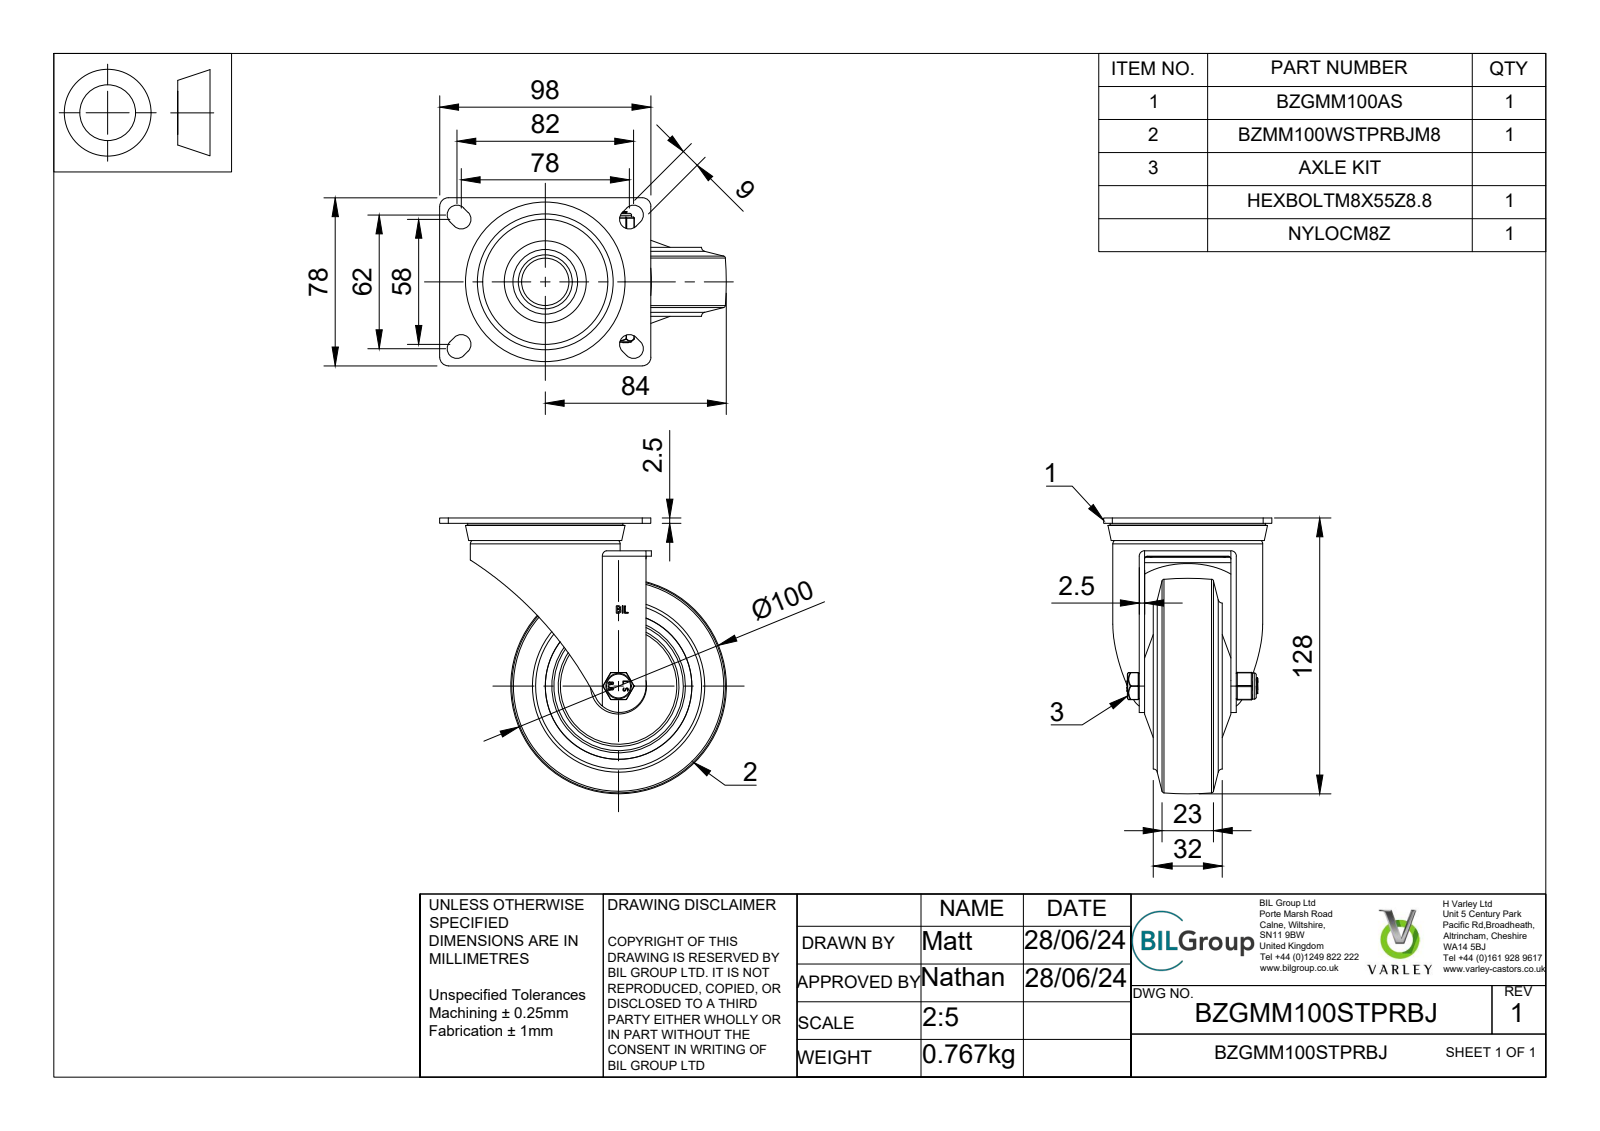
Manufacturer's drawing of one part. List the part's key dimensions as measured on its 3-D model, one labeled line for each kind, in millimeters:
Part name (STEP PRODUCT): BZGMM100STPRBJ v3; BZGMM100AS - 2 v1; ZINC PLATED, PRESSED STEEL TOP PLATE; ZINC PLATED, PRESSED STEEL TOP PLATE Geometry (+7 more)
STEP written by: Autodesk Translation Framework v13.14.0.145 (AUTOMOTIVE_DESIGN)
Units: millimetres
Bodies: 51 solids, 762 faces (272 planar, 190 cylindrical, 300 other)
Overall size (bounding box): 133 × 128 × 78
Volume: 257 703 mm³ · Surface area: 131 281 mm²
Round holes (diameter × count): ⌀0.66 ×2, ⌀30 ×2, ⌀8 ×1, ⌀8.2 ×1, ⌀8.6 ×1, ⌀11.5 ×1, ⌀15 ×1, ⌀20 ×1, ⌀22.5 ×1, ⌀26 ×1, ⌀31 ×1, ⌀32 ×1
Round bosses / shafts (diameter × count): ⌀69.5 ×1, ⌀56 ×1, ⌀47 ×1, ⌀44 ×1, ⌀35 ×1, ⌀30.5 ×1, ⌀25 ×1, ⌀23 ×1
Partial cylindrical surfaces — rounded edges, fillets, slot ends (radius × count): R0.5 ×18, R0.25 ×12, R4.5 ×8, R0.33 ×4, R0.64 ×4, R1.25 ×4, R4 ×4, R0.63 ×2
Main face-to-face distances: 2.5, 4, 3, 13.5, 17.5, 36, 7.5, 25, 6.5, 38.5
Hole centre spacings: 3.22, 2.49
